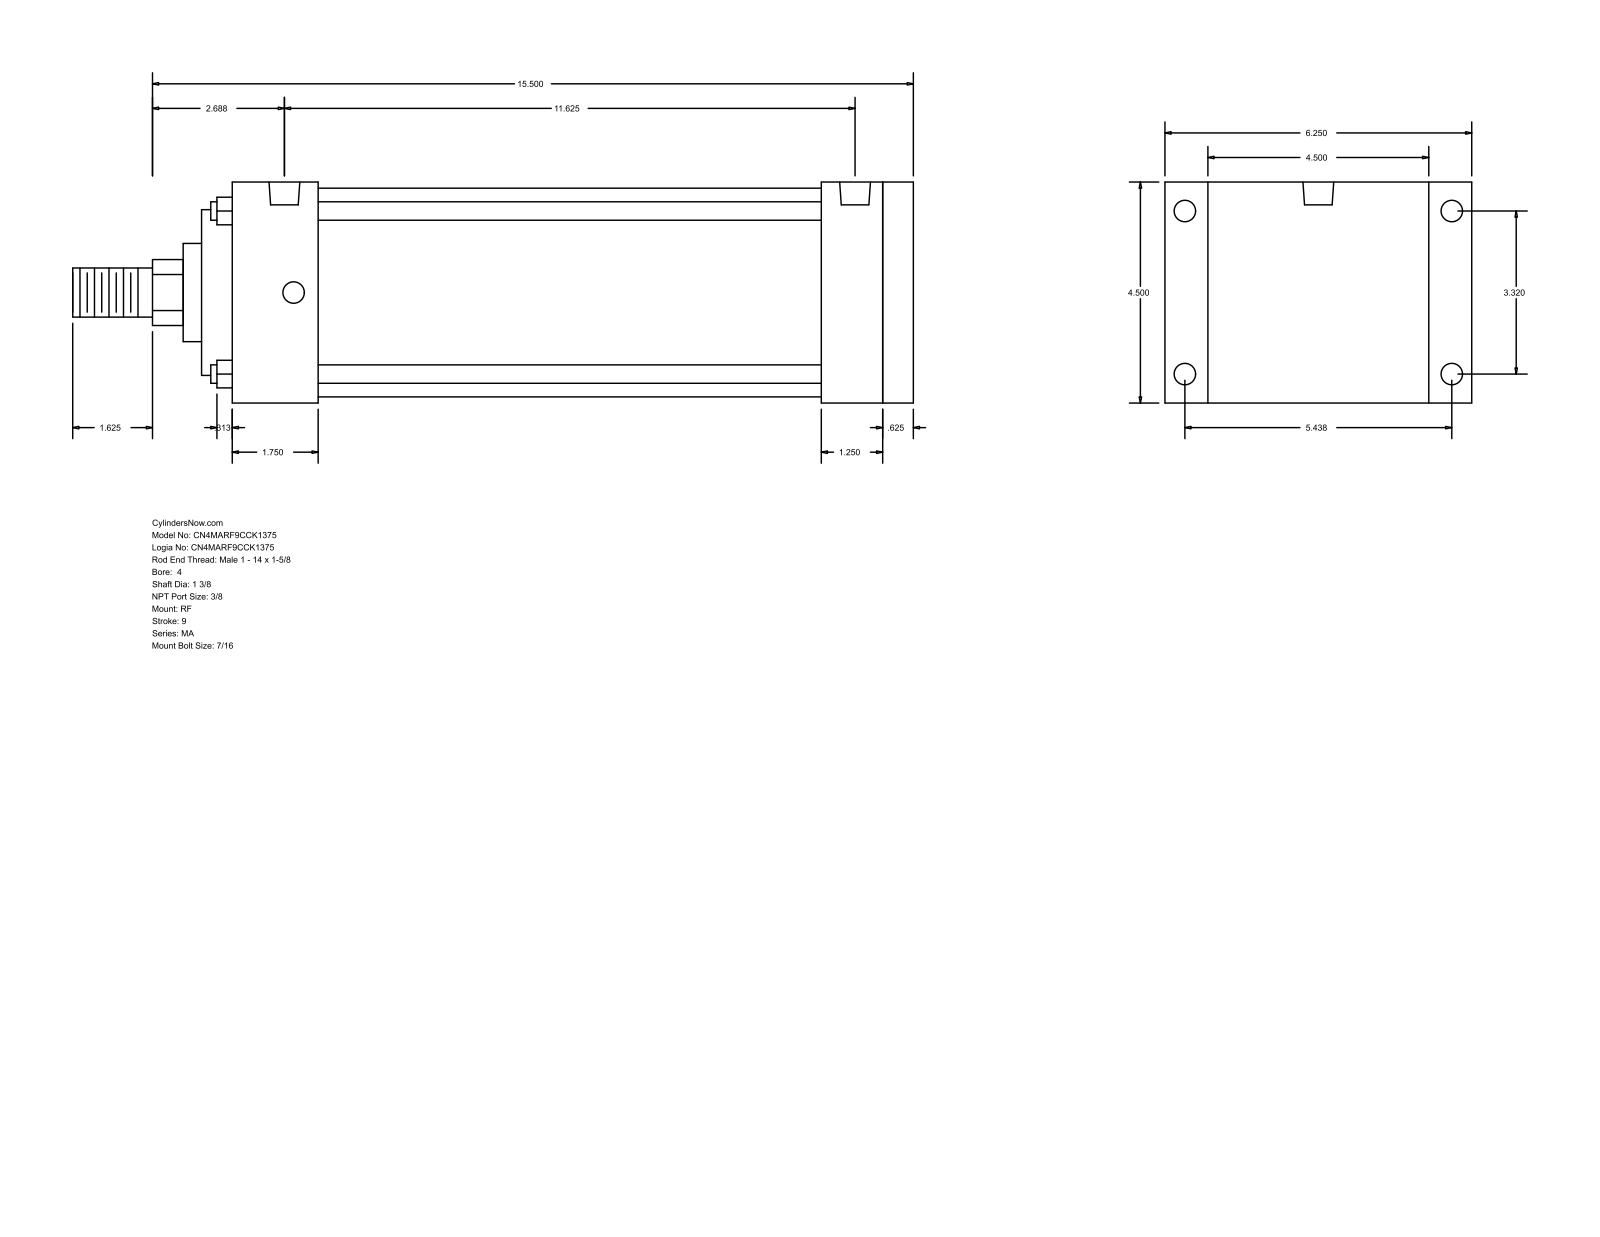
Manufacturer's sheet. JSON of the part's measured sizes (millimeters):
{"part_name": "MA_RF__0400_1.375", "step_written_by": "GSSL Pune (CONFIG_CONTROL_DESIGN)", "units": "millimeters", "bodies": {"solids": 0, "faces": 94, "planar": 65, "cylindrical": 29, "other": 0}, "overall_size": [434.98, 158.75, 114.3], "round_holes": [[11.11, 8], [15.93, 2]], "round_bosses_or_shafts": [[9.53, 4], [107.95, 1], [85.72, 1], [50.8, 1], [34.92, 1], [25.4, 1]], "partial_cylinders_radius": [[17.06, 1]], "face_to_face_distances": [114.3, 352.43, 15.88, 336.55, 15.87, 352.42, 368.3, 22.23, 136.53, 320.67], "hole_center_spacings": [4.77, 84.32, 138.12, 161.82, 285.74, 290.51, 295.28]}
